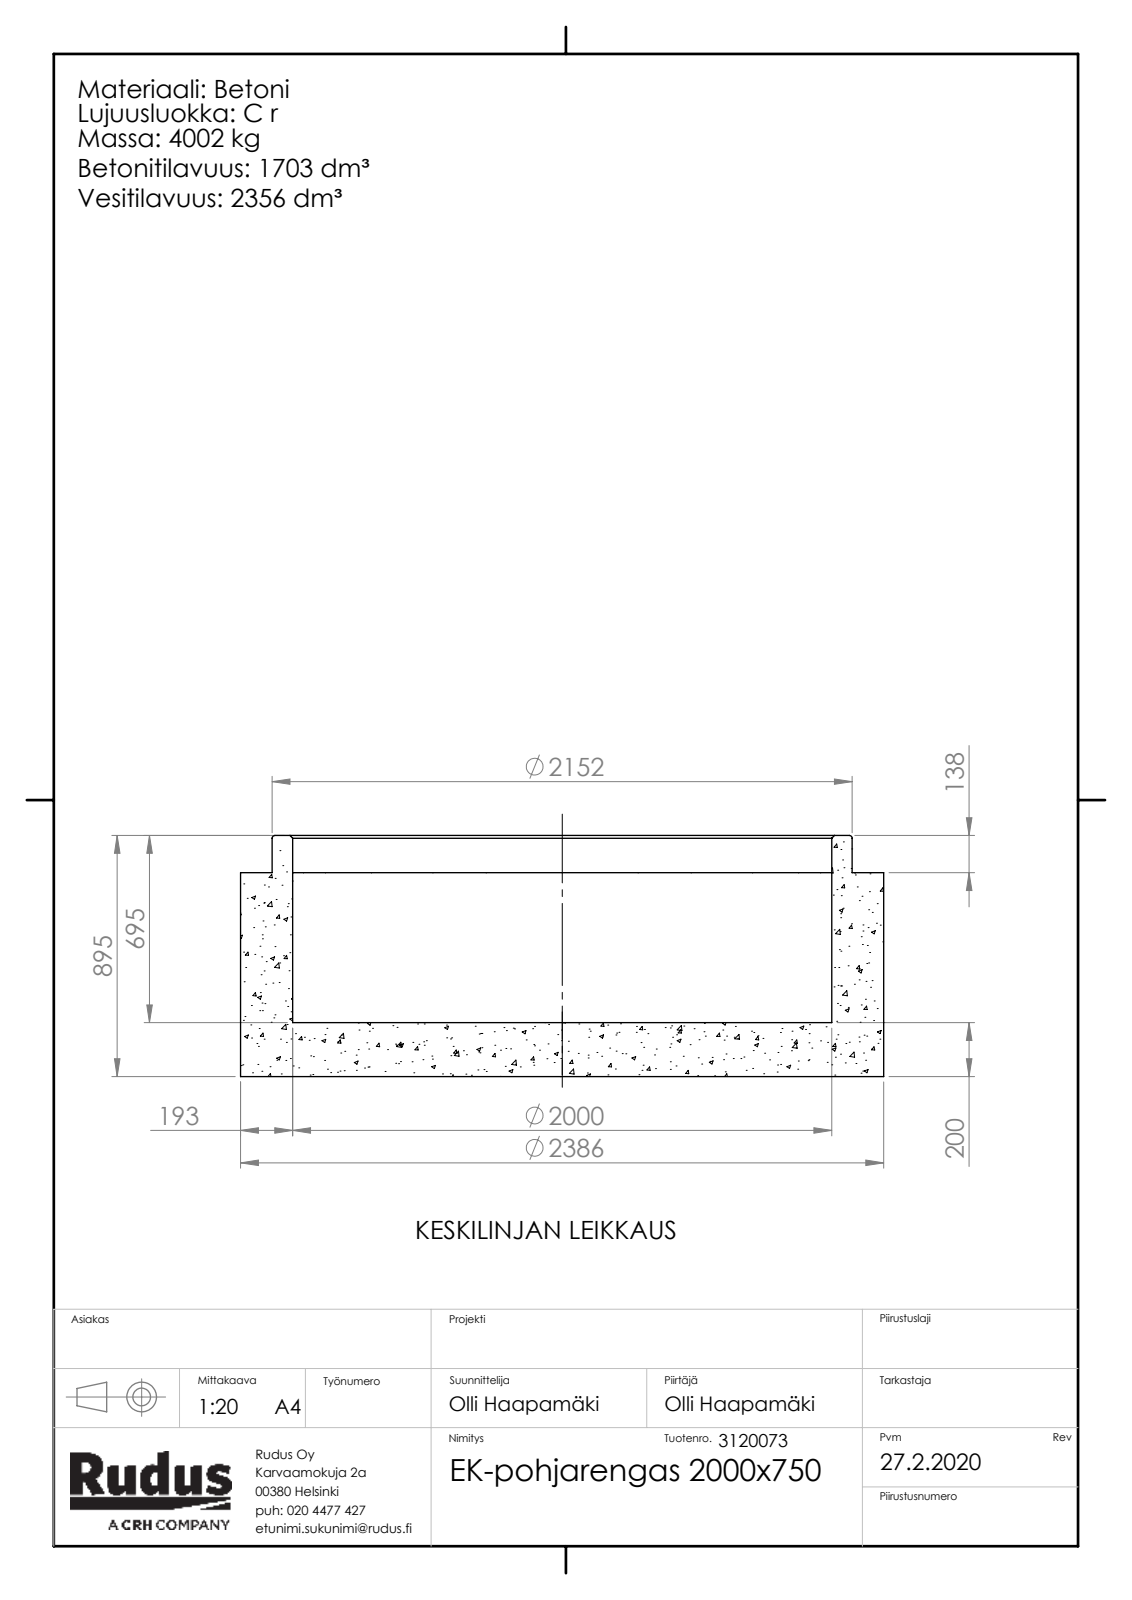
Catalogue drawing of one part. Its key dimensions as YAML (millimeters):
part_name: "EK-osa-kaivorunko_EK-pohjarengas; Rudus 3120073 EK-pohjarengas 2000x750"
step_written_by: "SolidWorks 2019 (CONFIG_CONTROL_DESIGN)"
units: millimeters
bodies: {solids: 1, faces: 95, planar: 5, cylindrical: 6, other: 84}
overall_size: [2386, 2386, 895]
volume: 1703000000
surface_area: 19860000
round_holes:
  - {diameter: 2000, count: 1}
round_bosses_or_shafts:
  - {diameter: 2386, count: 1}
  - {diameter: 2152, count: 1}
face_to_face_distances: [200, 757, 557, 895, 695, 138, 278.5, 478.5, 416.5]
